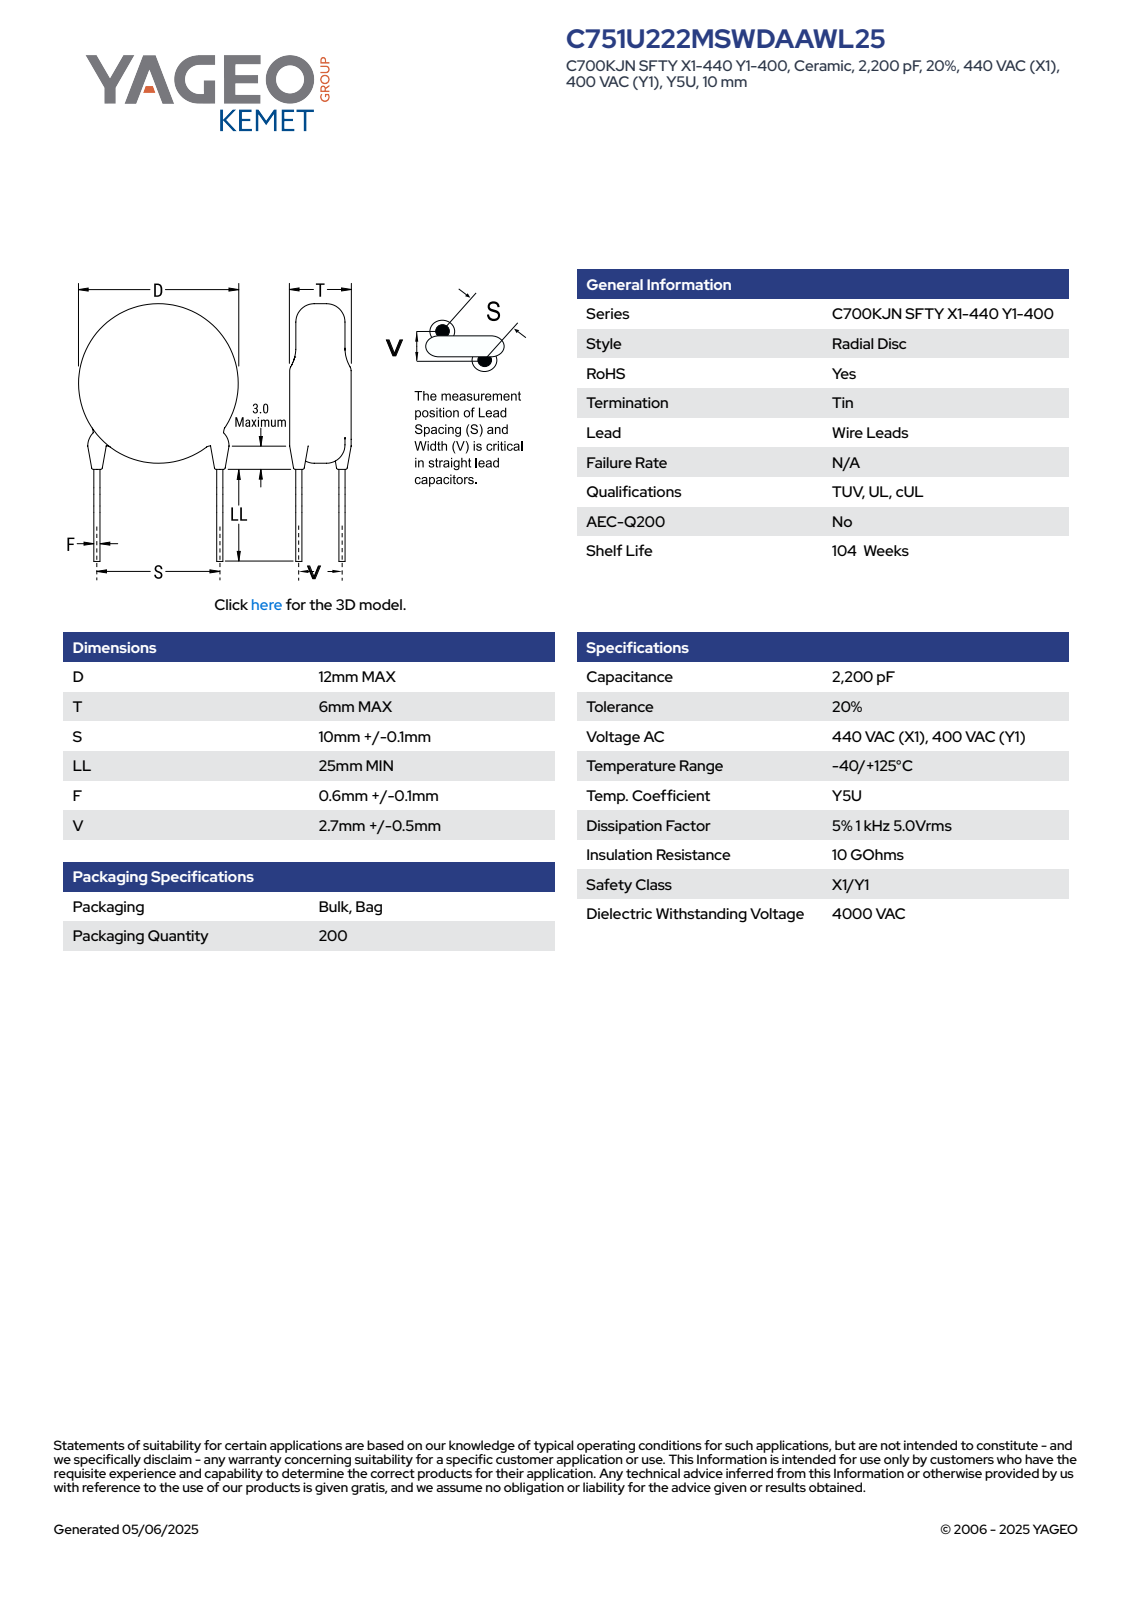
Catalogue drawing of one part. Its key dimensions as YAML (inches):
part_name: "CCD_KST_12X6_D12T6S10LL25F0.7V2.7"
step_written_by: "SolidWorks 2021 (AUTOMOTIVE_DESIGN)"
units: inches
bodies: {solids: 4, faces: 80, planar: 63, cylindrical: 13, other: 4}
overall_size: [1.486, 0.472, 0.236]
volume: 0.042
surface_area: 0.876
round_bosses_or_shafts:
  - {diameter: 0.047, count: 4}
  - {diameter: 0.028, count: 2}
  - {diameter: 0.472, count: 1}
face_to_face_distances: [0.236, 0.984, 1.286, 0.302, 1.232, 0.248, 0.054, 0.015, 0.043, 0.219]
